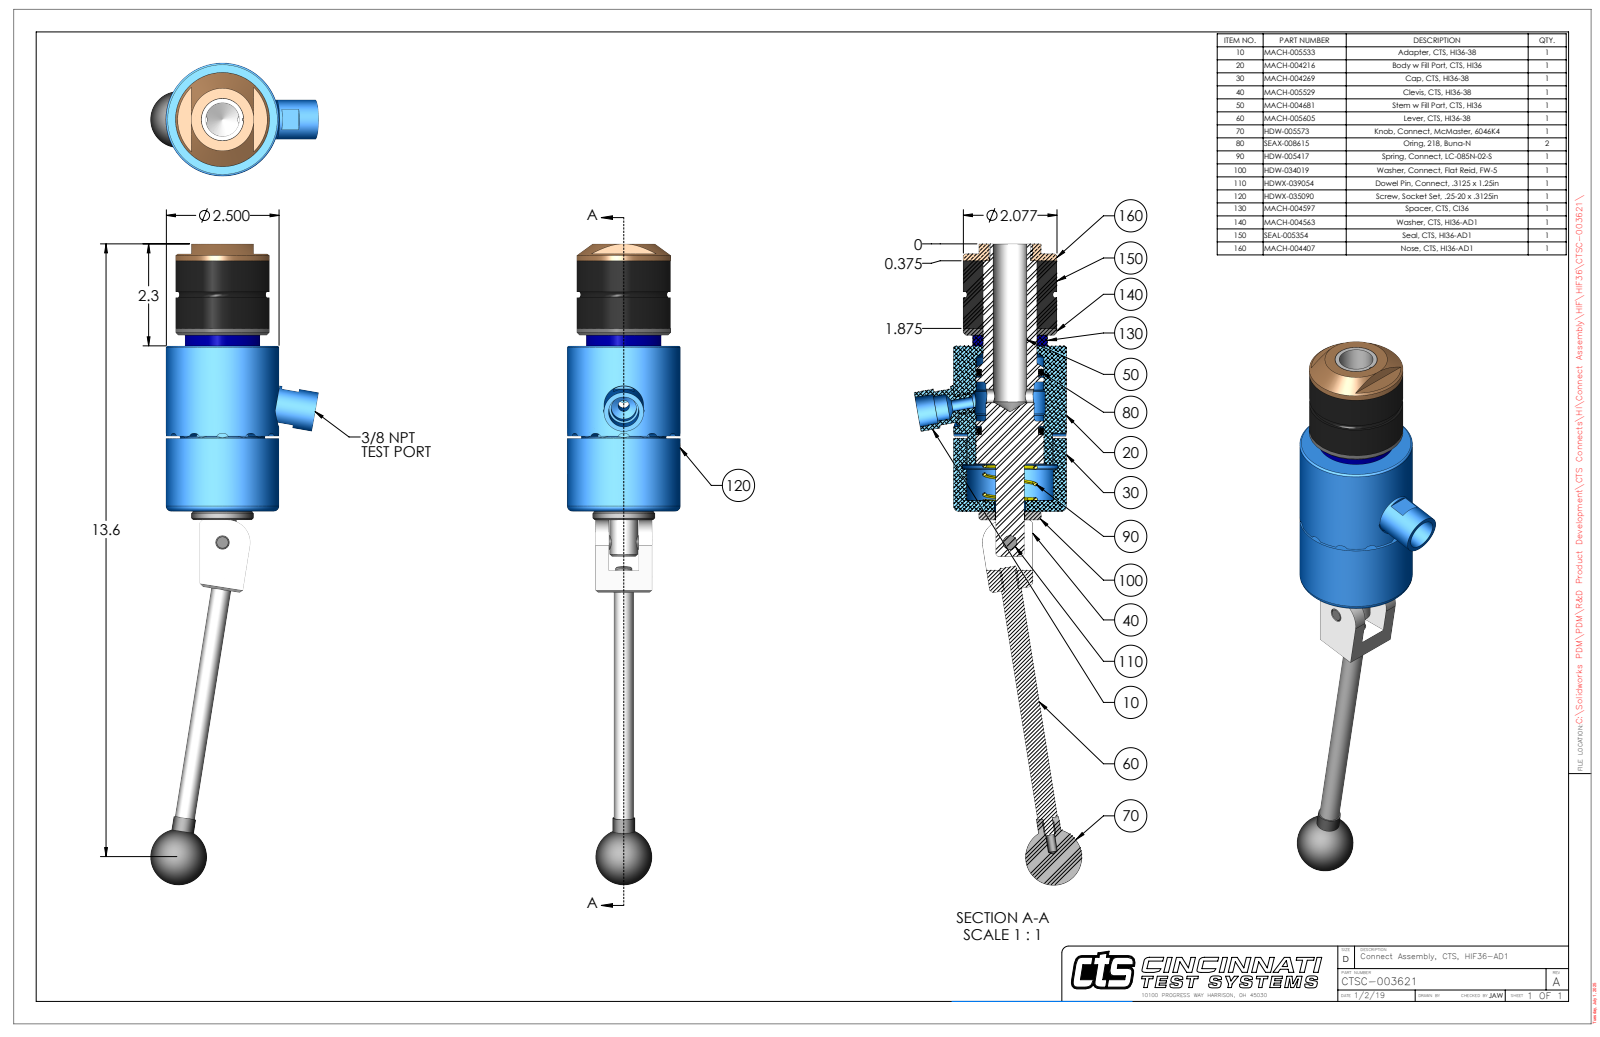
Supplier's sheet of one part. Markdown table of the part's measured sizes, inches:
| quantity | value |
| --- | --- |
| part name | CTSC-003621 |
| STEP written by | SolidWorks 2023 (AUTOMOTIVE_DESIGN) |
| units | inches |
| bodies | 10 solids, 308 faces (110 planar, 127 cylindrical, 71 other) |
| overall size | 14.215 × 3.716 × 2.5 |
| volume | 27.08 in³ |
| surface area | 135.7 in² |
| round holes (diameter × count) | 0.201 × 2, 0.15 × 1, 0.25 × 1, 0.311 × 1, 0.312 × 1, 0.313 × 1, 0.314 × 1, 0.562 × 1, 0.656 × 1, 0.696 × 1, 0.75 × 1, 0.922 × 1 |
| round bosses / shafts (diameter × count) | 2.5 × 1, 2.077 × 1, 1.875 × 1, 1.656 × 1, 1.38 × 1, 1.186 × 1, 1 × 1, 0.904 × 1 |
| partial cylindrical surfaces (radius × count) | 0.12 × 12, 0.029 × 2, 0.19 × 1, 0.195 × 1, 0.447 × 1, 0.47 × 1, 0.5 × 1, 1.182 × 1 |
| main face-to-face distances | 5.555, 4.055, 1.5, 3.668, 0.387, 1.887, 3.905, 0.237, 0.15, 1.65 |
| hole center spacings | 0.74, 2.118, 2.858 |
